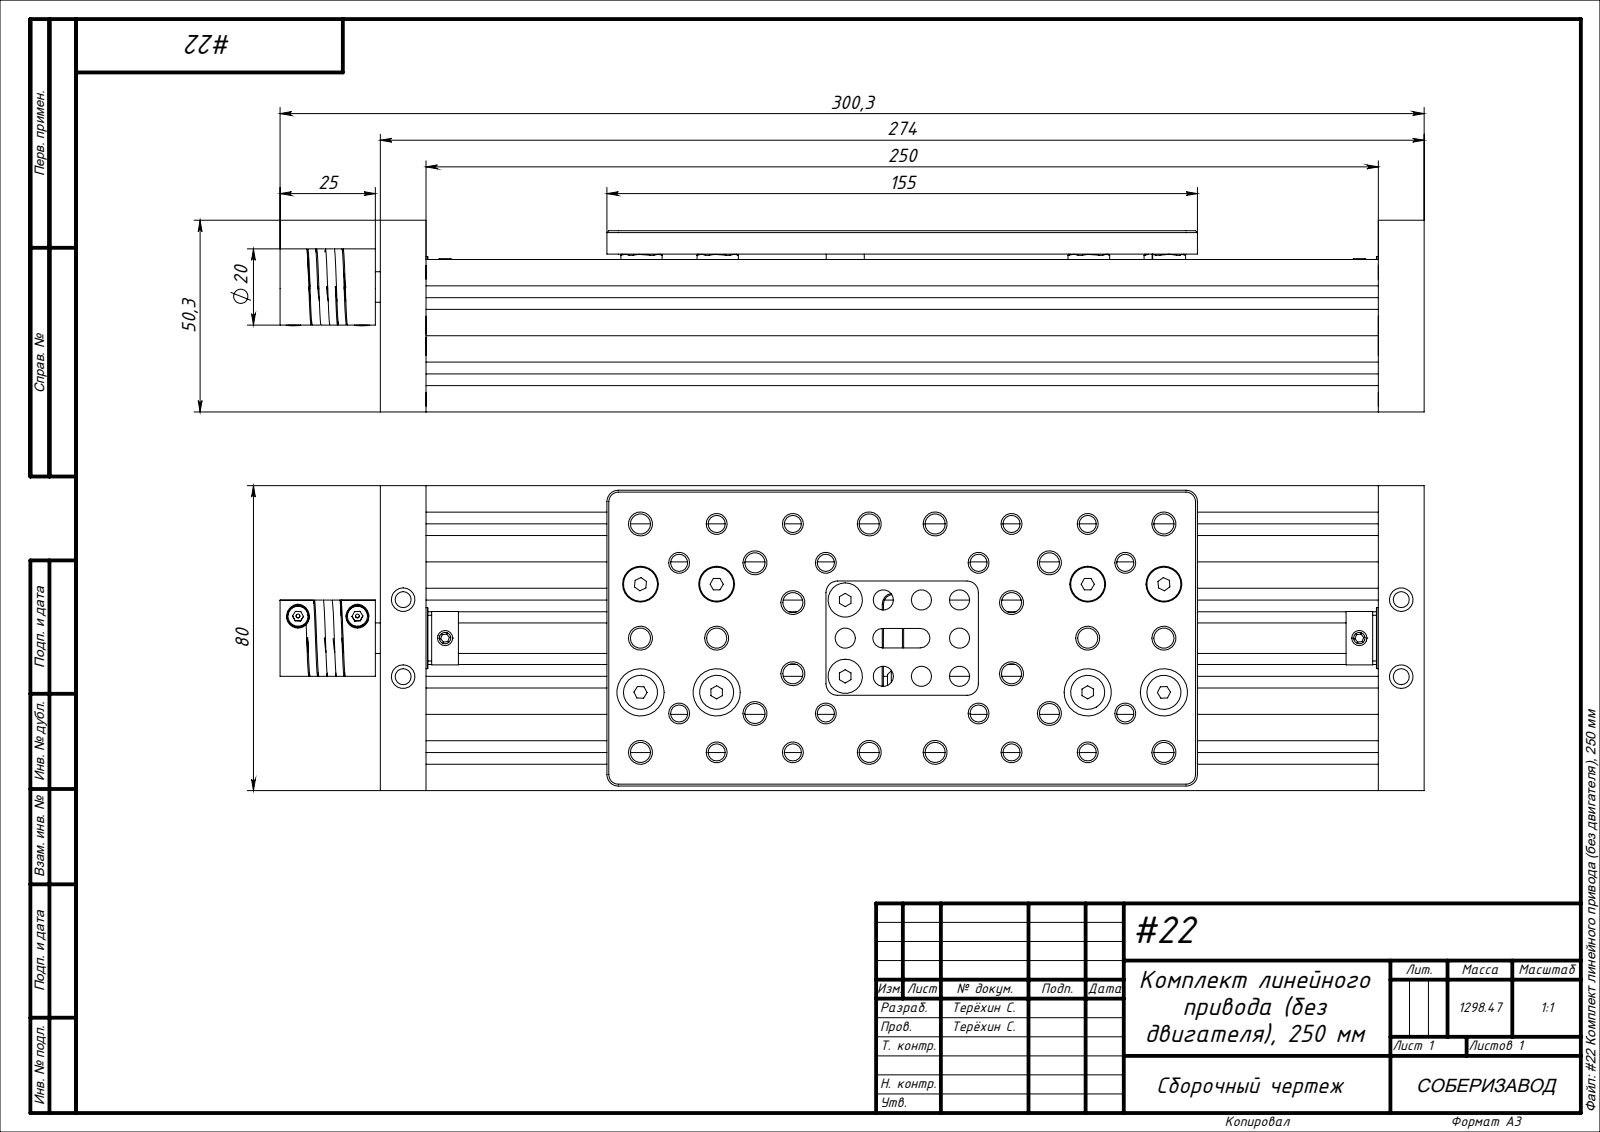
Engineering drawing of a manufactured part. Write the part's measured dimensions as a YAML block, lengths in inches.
part_name: "A213 Ограничительная шайба O 8 O 14; A213 Ограничительная шайба O 8 O 14_00; A229 Самоконтрящаяся гайка M5_00; Гайка М5, низкая DIN 439, K32_00 (+8 more)"
step_written_by: "SolidWorks 2021 (AUTOMOTIVE_DESIGN)"
units: inches
bodies: {solids: 171, faces: 4603, planar: 1282, cylindrical: 1432, other: 1889}
overall_size: [11.823, 3.15, 1.98]
volume: 26.56
surface_area: 491.6
round_holes:
  - {diameter: 0.209, count: 48}
  - {diameter: 0.177, count: 16}
  - {diameter: 0.197, count: 16}
  - {diameter: 0.165, count: 11}
  - {diameter: 0.163, count: 10}
  - {diameter: 0.203, count: 10}
  - {diameter: 0.24, count: 8}
  - {diameter: 0.307, count: 8}
  - {diameter: 0.331, count: 8}
  - {diameter: 0.341, count: 8}
  - {diameter: 0.394, count: 8}
  - {diameter: 0.205, count: 4}
round_bosses_or_shafts:
  - {diameter: 0.315, count: 14}
  - {diameter: 0.308, count: 10}
  - {diameter: 0.6, count: 8}
  - {diameter: 0.352, count: 8}
  - {diameter: 0.34, count: 8}
  - {diameter: 0.276, count: 8}
  - {diameter: 0.247, count: 8}
  - {diameter: 0.236, count: 8}
partial_cylinders:
  - {radius: 0.01, count: 100}
  - {radius: 0.008, count: 86}
  - {radius: 0.079, count: 48}
  - {radius: 0.039, count: 40}
  - {radius: 0.012, count: 30}
  - {radius: 0.055, count: 20}
  - {radius: 0.118, count: 8}
  - {radius: 0.059, count: 6}
face_to_face_distances: [0.557, 1.113, 0.472, 0.787, 0.071, 0.236, 0.486, 0.551, 1.67, 0.111]
hole_center_spacings: [0.787, 0.394, 0.881, 2.122, 0.789, 0.881, 1.115, 1.117]
